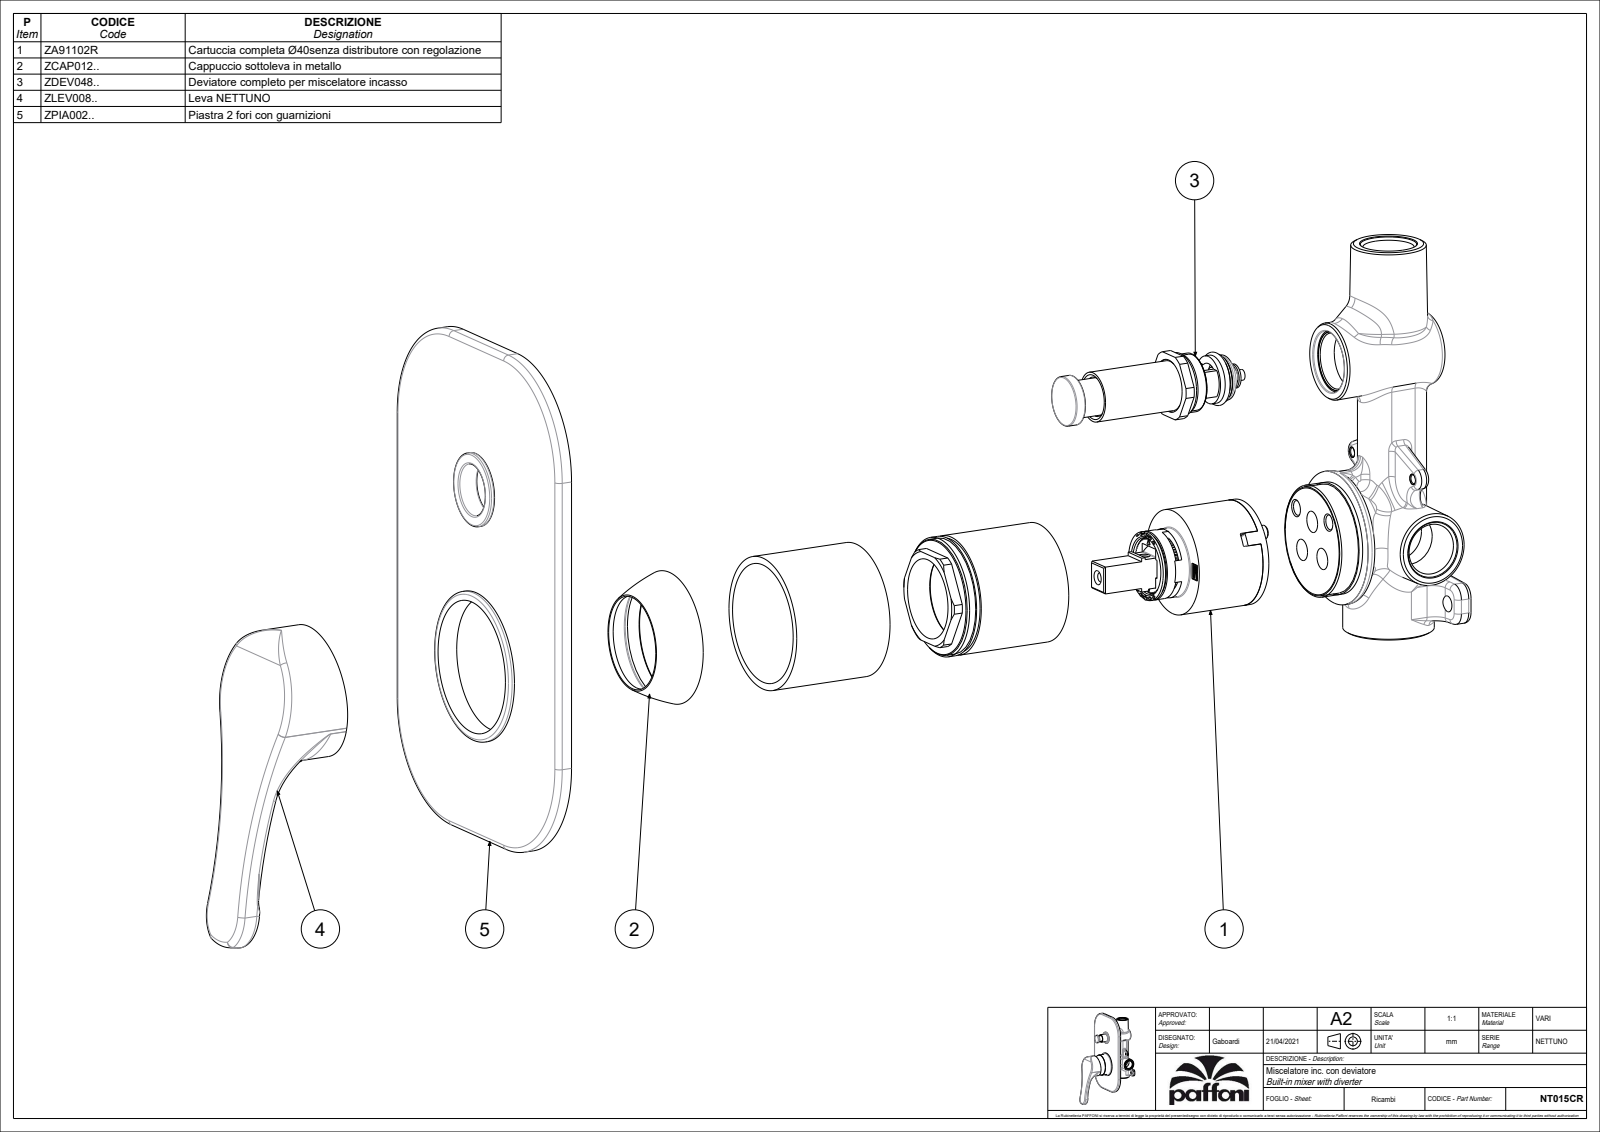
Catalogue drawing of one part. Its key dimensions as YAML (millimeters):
part_name: "NT015CR"
step_written_by: "CREO PARAMETRIC BY PTC INC, 2020044 (CONFIG_CONTROL_DESIGN)"
units: millimeters
bodies: {solids: 7, faces: 991, planar: 551, cylindrical: 260, other: 180}
overall_size: [217.68, 120.5, 76.69]
volume: 101000
surface_area: 100332
round_holes:
  - {diameter: 3, count: 1}
  - {diameter: 3.3, count: 1}
  - {diameter: 4, count: 1}
  - {diameter: 4.5, count: 1}
  - {diameter: 5, count: 1}
  - {diameter: 6, count: 1}
  - {diameter: 9.4, count: 1}
  - {diameter: 10.5, count: 1}
  - {diameter: 14.8, count: 1}
  - {diameter: 19.1, count: 1}
  - {diameter: 21, count: 1}
  - {diameter: 21.2, count: 1}
round_bosses_or_shafts:
  - {diameter: 56.5, count: 1}
  - {diameter: 55, count: 1}
  - {diameter: 50.3, count: 1}
  - {diameter: 50, count: 1}
  - {diameter: 44.8, count: 1}
  - {diameter: 43, count: 1}
  - {diameter: 39.5, count: 1}
  - {diameter: 33, count: 1}
partial_cylinders:
  - {radius: 0.2, count: 24}
  - {radius: 0.5, count: 22}
  - {radius: 2, count: 8}
  - {radius: 1, count: 5}
  - {radius: 1.2, count: 4}
  - {radius: 39.2, count: 4}
  - {radius: 40, count: 4}
  - {radius: 135, count: 2}
face_to_face_distances: [0.8, 6, 5.2, 14.5, 2.8, 119.7, 22.5, 55.25, 65.25, 54.45]
hole_center_spacings: [9.9, 67.97, 68]
